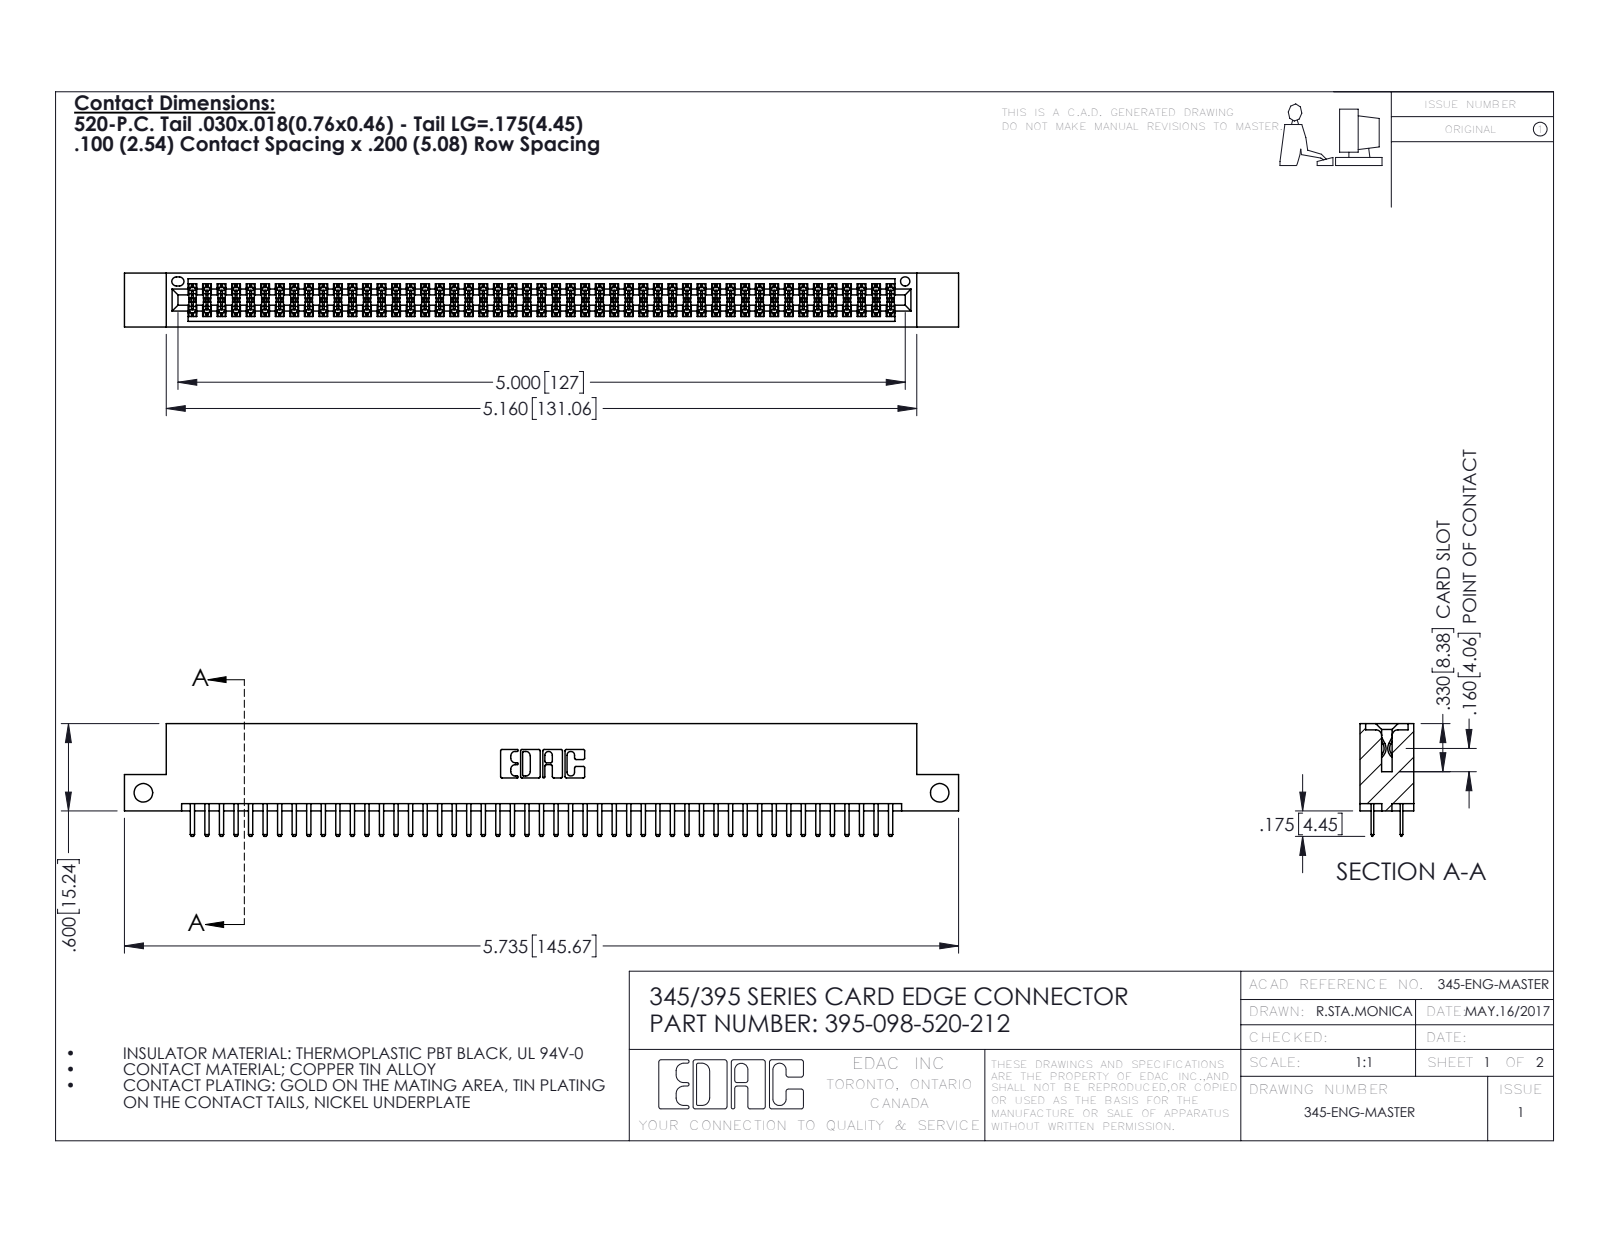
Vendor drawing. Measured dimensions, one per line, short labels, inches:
name: 395-098-520-212; 345-292-001_345-293-120; 345 Part_Flush Mounting Lugs - Side Mount
written by: SolidWorks 2016 (CONFIG_CONTROL_DESIGN)
unit: in
bodies: 99 solids, 5418 faces (3510 planar, 1908 cylindrical, 0 other)
size: 5.735 × 0.775 × 0.37
volume: 0.86 in³; area: 32.13 in²
holes: 2× ⌀0.128, 1× ⌀0.064
rounds: 147× R0.006, 102× R0.01, 22× R0.01, 6× R0.007, 6× R0.031, 3× R0.026, 2× R0.014, 2× R0.019
face distances: 0.298, 0.072, 0.2, 0.37, 0.098, 0.272, 0.025, 0.225, 0.022, 0.072
hole spacings: 5.475
